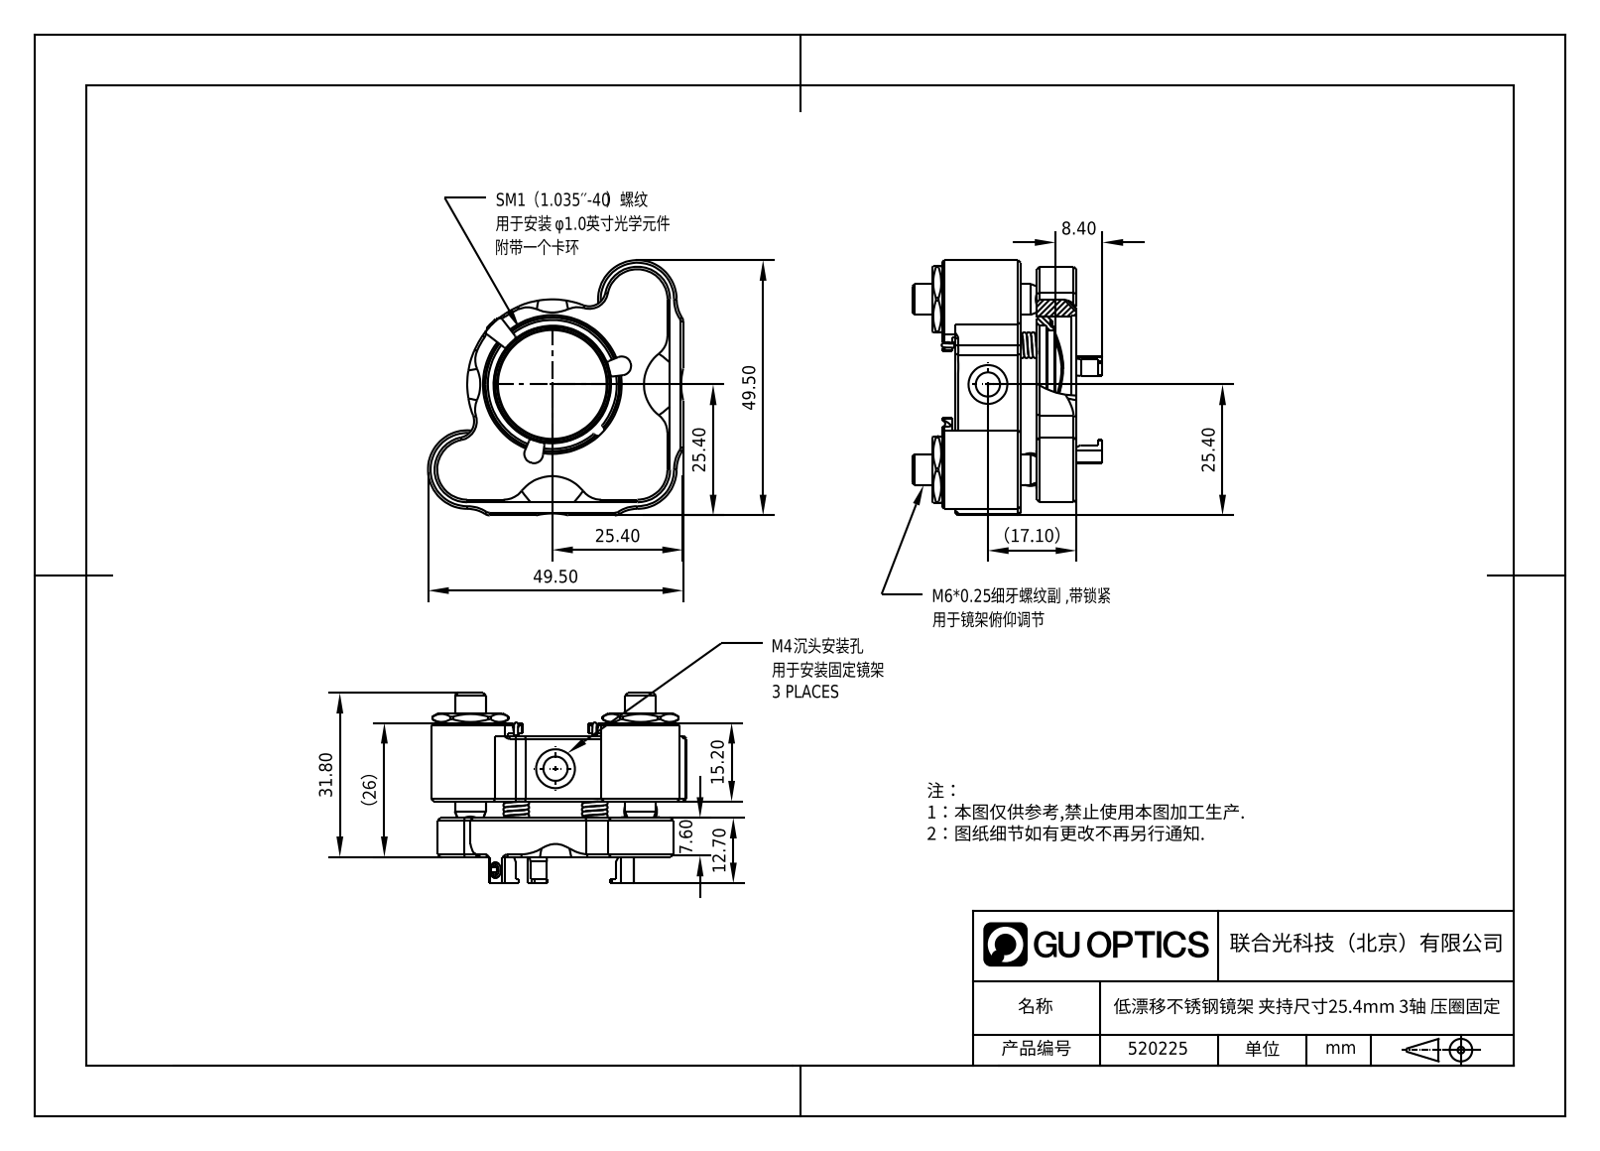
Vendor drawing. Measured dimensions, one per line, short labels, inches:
name: DXS-0625标准型细牙螺丝_3.2.2.16-DXS-0625-26.6; 标准细牙锁紧螺母，外六角_3.2.6.14_DXJ-S0625-1302; ZFK不锈钢透镜卡环压圈_1.8.9.2_ZFKS-K1.0; 1.1.20.26.1_替代进口不锈钢光学调整架前面板，低变形，SM1.0，含一个卡环，两轴 (+3 more)
written by: SolidWorks 2021 (CONFIG_CONTROL_DESIGN)
unit: in
bodies: 24 solids, 669 faces (188 planar, 185 cylindrical, 296 other)
size: 1.95 × 1.95 × 1.54
volume: 1.31 in³; area: 27.2 in²
holes: 7× ⌀0.25, 5× ⌀0.098, 3× ⌀0.157, 3× ⌀0.236, 2× ⌀0.079, 2× ⌀0.185, 2× ⌀0.297, 1× ⌀0.079, 1× ⌀0.941, 1× ⌀1.035, 1× ⌀1.06
bosses: 6× ⌀0.157, 2× ⌀0.6, 1× ⌀0.118
rounds: 18× R0.024, 14× R0.255, 8× R0.02, 4× R0.039, 4× R0.07, 4× R0.076, 3× R0.25, 2× R0.063
face distances: 0.425, 0.1, 0.6, 1.025, 0.3, 0.125, 0.725, 0.5, 0.625, 0.925
hole spacings: 0.35, 0.594, 0.6, 0.716, 0.95, 0.919, 0.197, 0.523
